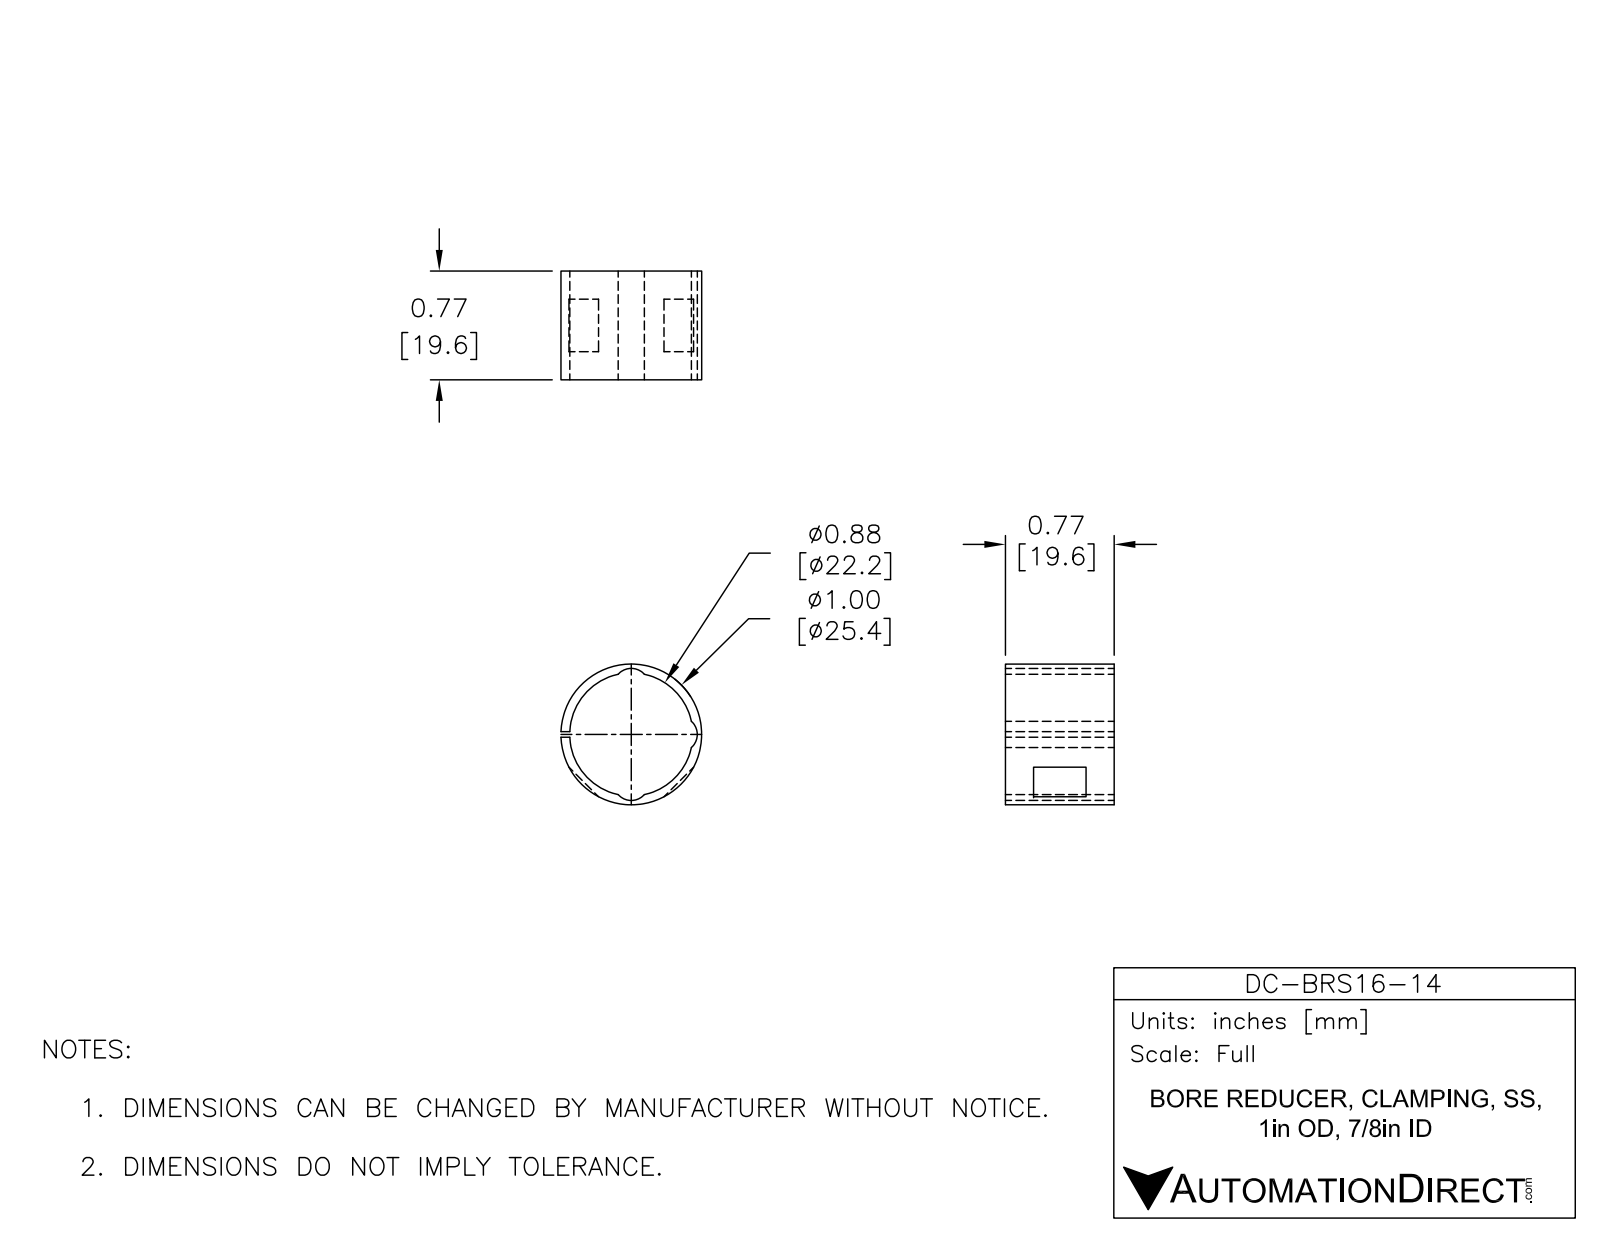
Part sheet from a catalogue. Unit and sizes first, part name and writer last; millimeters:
Units: millimetres
Overall size (bounding box): 31.75 × 31.74 × 20.14
Round bosses / shafts (diameter × count): ⌀31.75 ×1
Partial cylindrical surfaces — rounded edges, fillets, slot ends (radius × count): R3.17 ×3, R11 ×1
Main face-to-face distances: 20.14, 1.02, 6.34, 2.66, 3.68, 5.33, 14.81, 9.48
Volume: 6 758 mm³ · Surface area: 4 625 mm²
Bodies: 1 solid, 27 faces (16 planar, 11 cylindrical, 0 other)
Part name (STEP PRODUCT): DC-BRS16-14
STEP written by: SolidWorks 2015 (AUTOMOTIVE_DESIGN)
